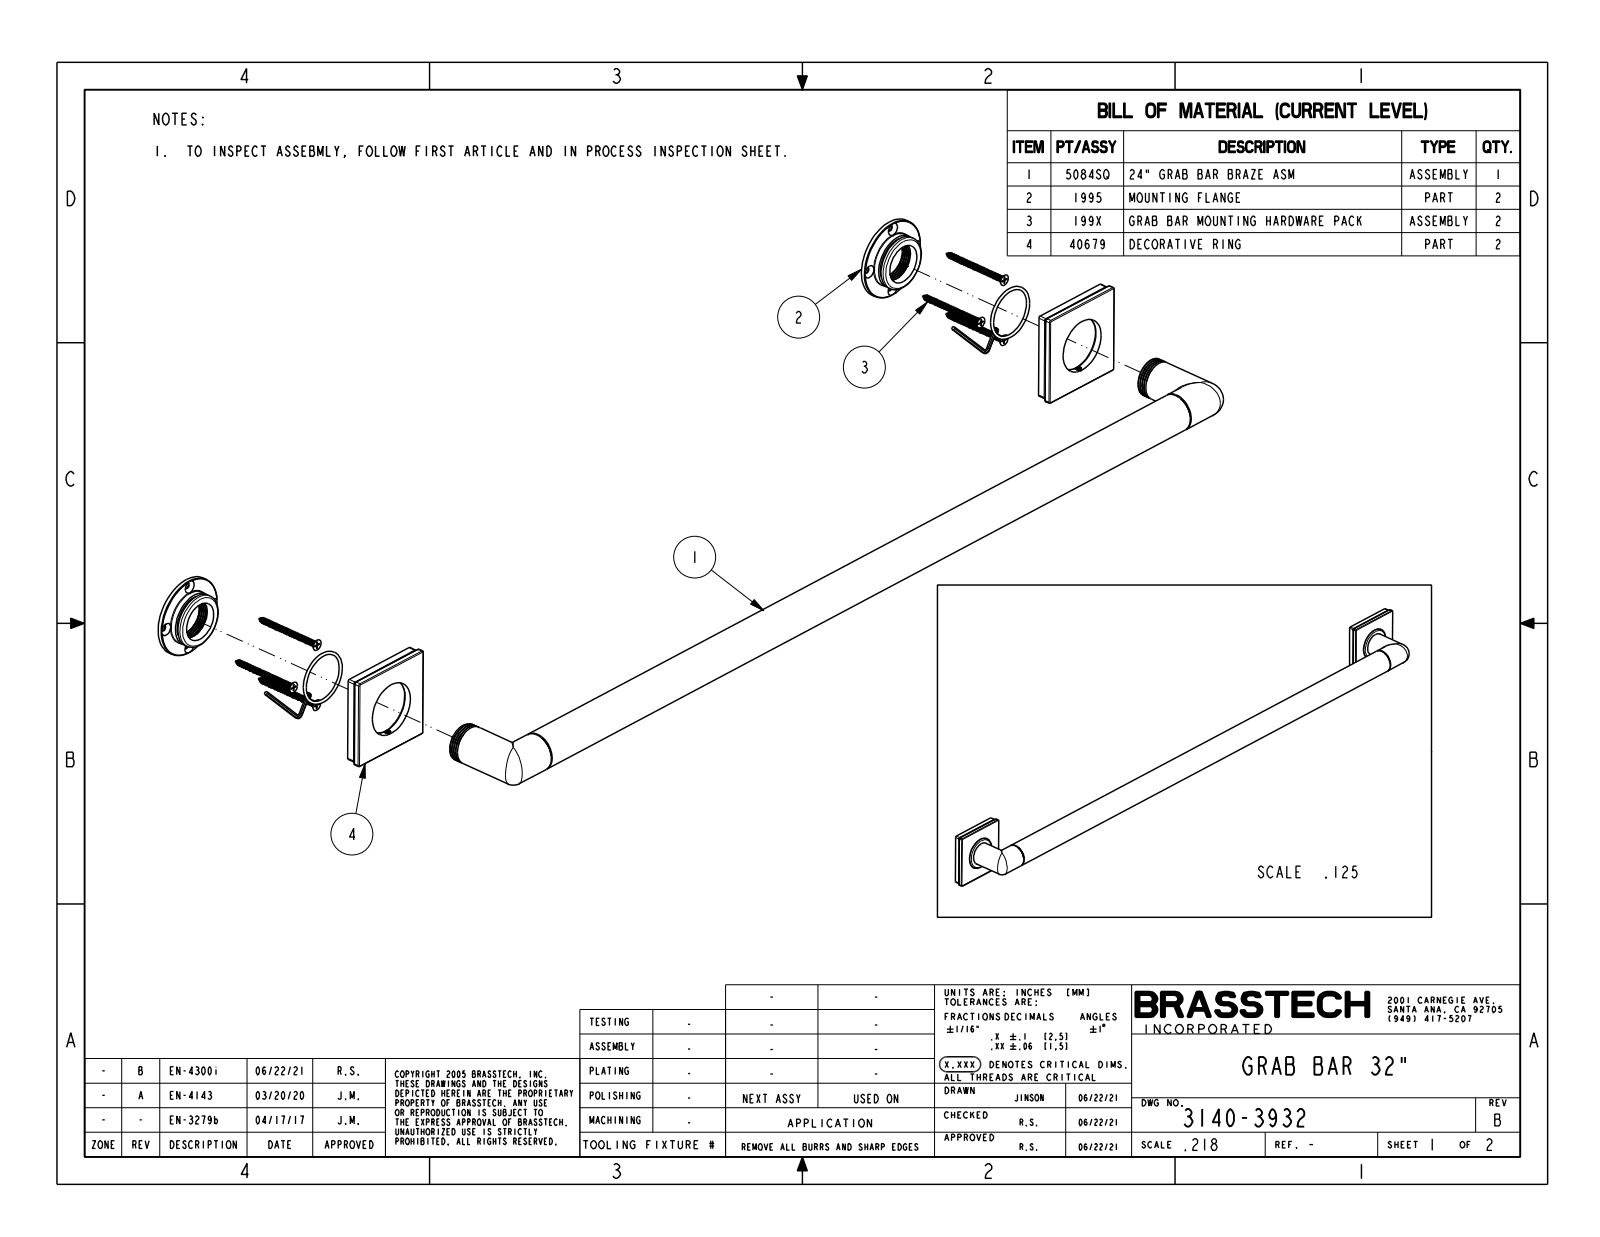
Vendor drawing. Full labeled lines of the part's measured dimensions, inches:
Part name (STEP PRODUCT): 3140-3932
STEP written by: CREO PARAMETRIC BY PTC INC, 2018400 (CONFIG_CONTROL_DESIGN)
Units: inches
Bodies: 1 solid, 168 faces (22 planar, 54 cylindrical, 92 other)
Overall size (bounding box): 35 × 3 × 2.755
Volume: 52.41 in³ · Surface area: 182.6 in²
Round bosses / shafts (diameter × count): ⌀1.25 ×3, ⌀1.75 ×2
Partial cylindrical surfaces — rounded edges, fillets, slot ends (radius × count): R0.06 ×16, R0.03 ×12, R0.09 ×6
Main face-to-face distances: 0.525, 0.05, 2.95, 2.9, 32, 3, 0.6, 0.075, 32.05, 34.95
